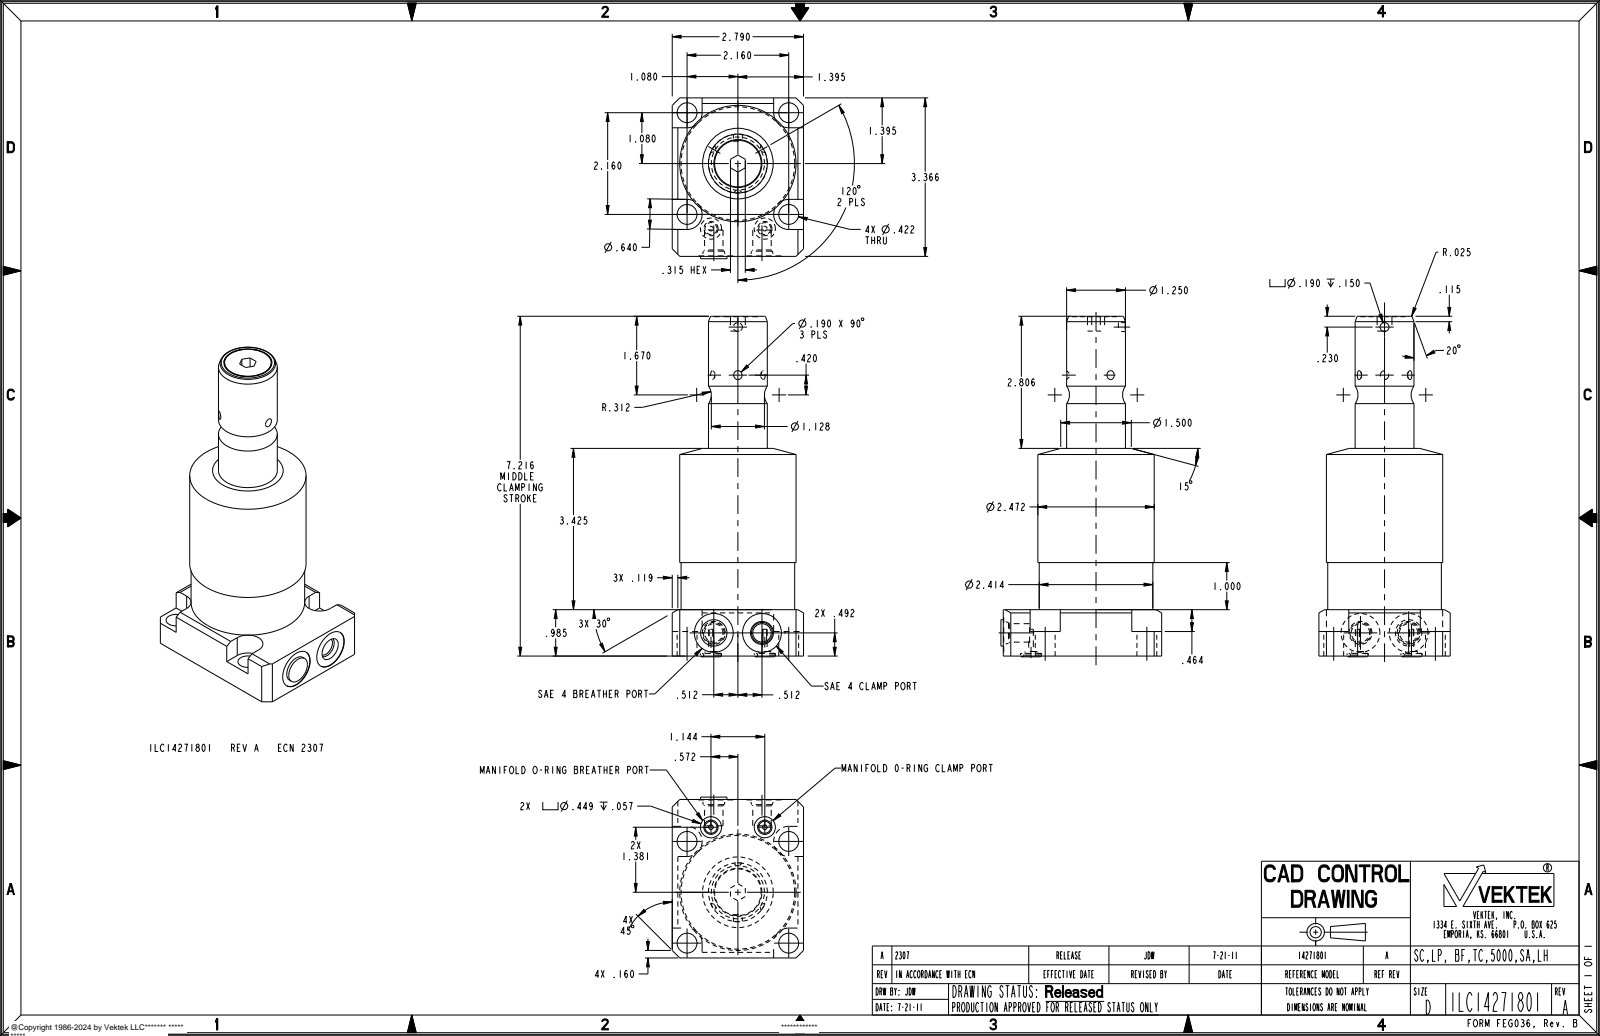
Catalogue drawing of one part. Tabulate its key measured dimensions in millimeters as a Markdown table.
| quantity | value |
| --- | --- |
| part name | ILC14271801 |
| STEP written by | PRO/ENGINEER BY PARAMETRIC TECHNOLOGY CORPORATION, 2007460 (AUTOMOTIVE_DESIGN_CC2) |
| units | millimeters |
| bodies | 1 solid, 135 faces (55 planar, 50 cylindrical, 30 other) |
| overall size | 183.7 × 86.8 × 70.9 |
| volume | 448 800 mm³ |
| surface area | 46 970 mm² |
| round holes (diameter × count) | 10.7 × 4, 2.5 × 2, 6.5 × 2, 10 × 2, 11.4 × 2, 21 × 2, 4.8 × 1, 25.9 × 1 |
| round bosses / shafts (diameter × count) | 62.8 × 1, 61.3 × 1, 31.8 × 1, 25.1 × 1, 14.2 × 1 |
| partial cylindrical surfaces (radius × count) | 8.1 × 4 |
| main face-to-face distances | 25, 70.9, 85.5, 11.8, 13.2, 158.3, 170.1, 183.3, 85.2, 54.7 |
| hole center spacings | 38.8, 54.9, 15, 38, 42.6, 63.8, 75.3, 77.6 |
